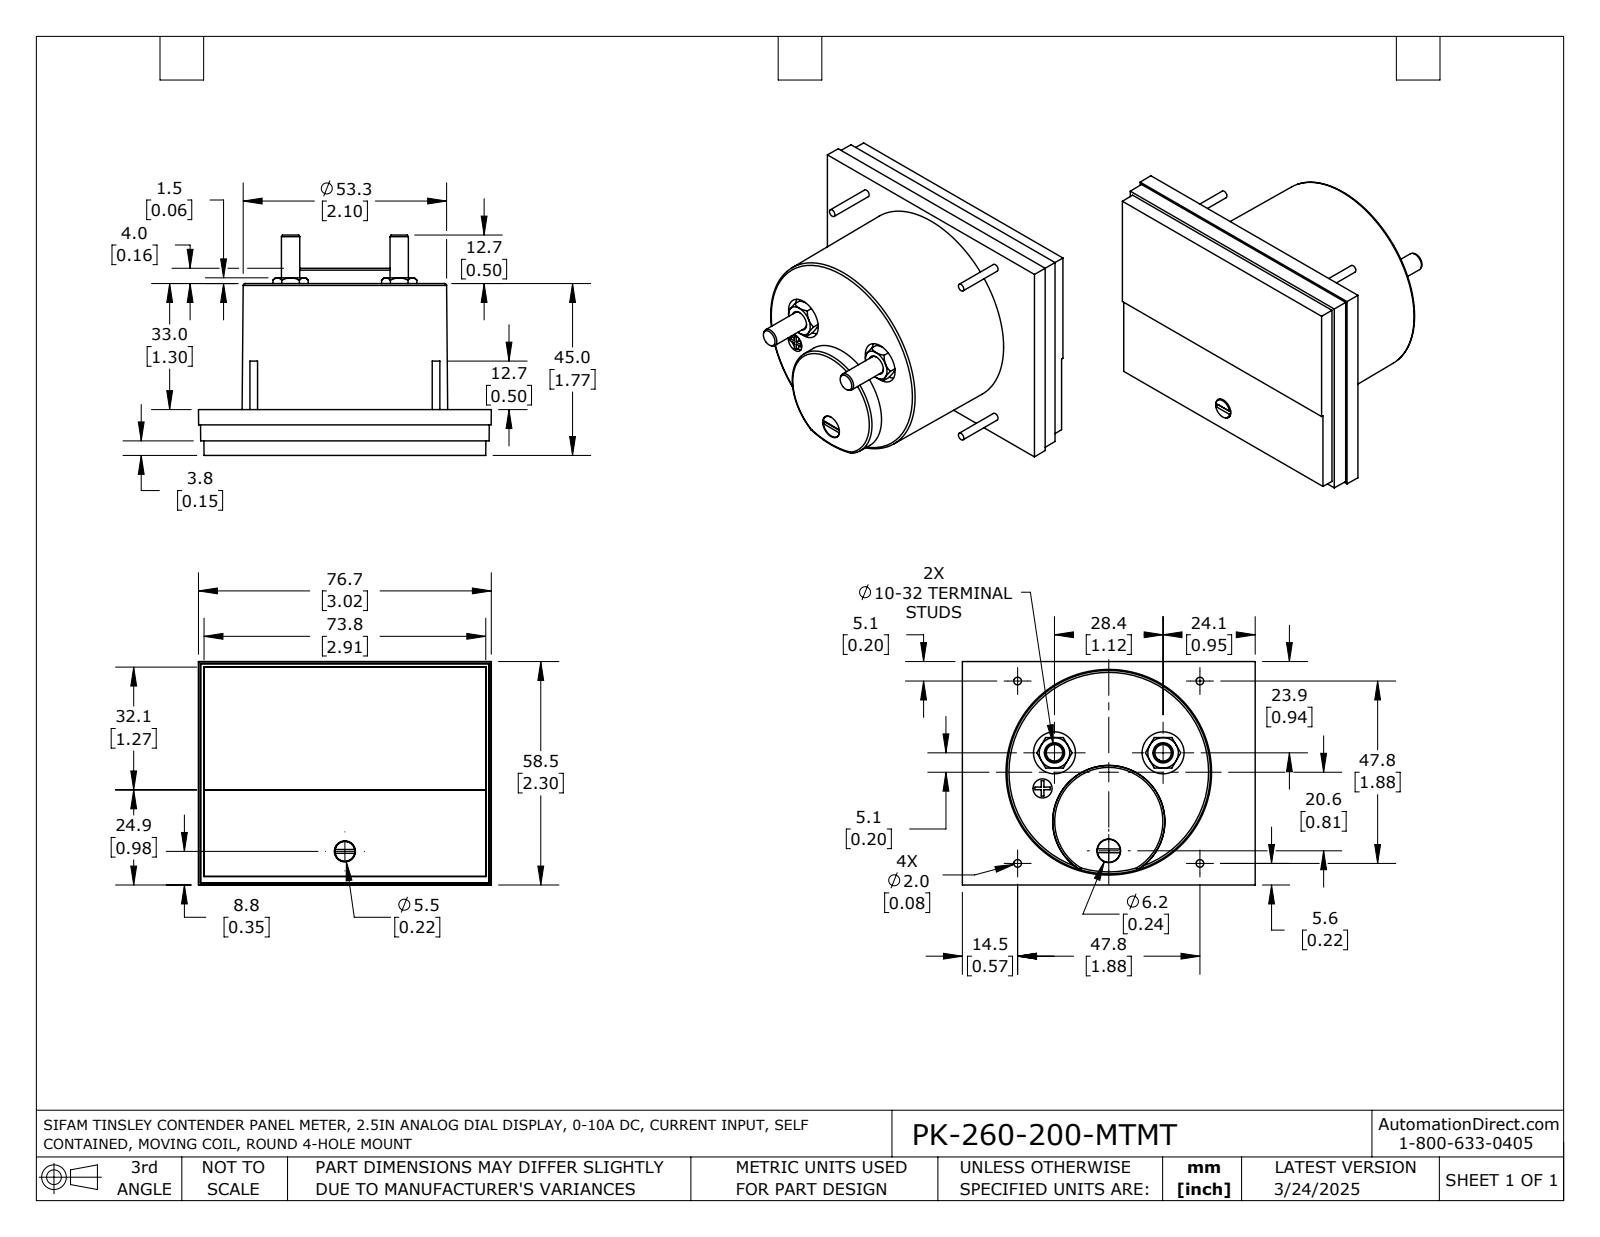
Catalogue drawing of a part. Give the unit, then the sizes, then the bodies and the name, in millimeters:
Units: millimetres
Overall size (bounding box): 76.7 × 58.5 × 57.7
Round holes (diameter × count): ⌀5 ×3, ⌀11 ×2, ⌀5.3 ×1, ⌀5.5 ×1, ⌀6.2 ×1
Round bosses / shafts (diameter × count): ⌀2 ×4, ⌀4.8 ×2, ⌀6 ×1, ⌀5.2 ×1
Partial cylindrical surfaces — rounded edges, fillets, slot ends (radius × count): R0.8 ×1
Main face-to-face distances: 0.5, 12, 3.3, 8.2, 3.8, 11.5, 1.4, 2, 10.1, 1.9
Hole centre spacings: 29.3, 29.5, 9.8, 23.8, 23.9, 28.4, 32.9
Volume: 125 500 mm³ · Surface area: 23 580 mm²
Bodies: 1 solid, 192 faces (95 planar, 37 cylindrical, 60 other)
Part name (STEP PRODUCT): PK-260-200-MTMT
STEP written by: SolidWorks 2021 (AUTOMOTIVE_DESIGN)
